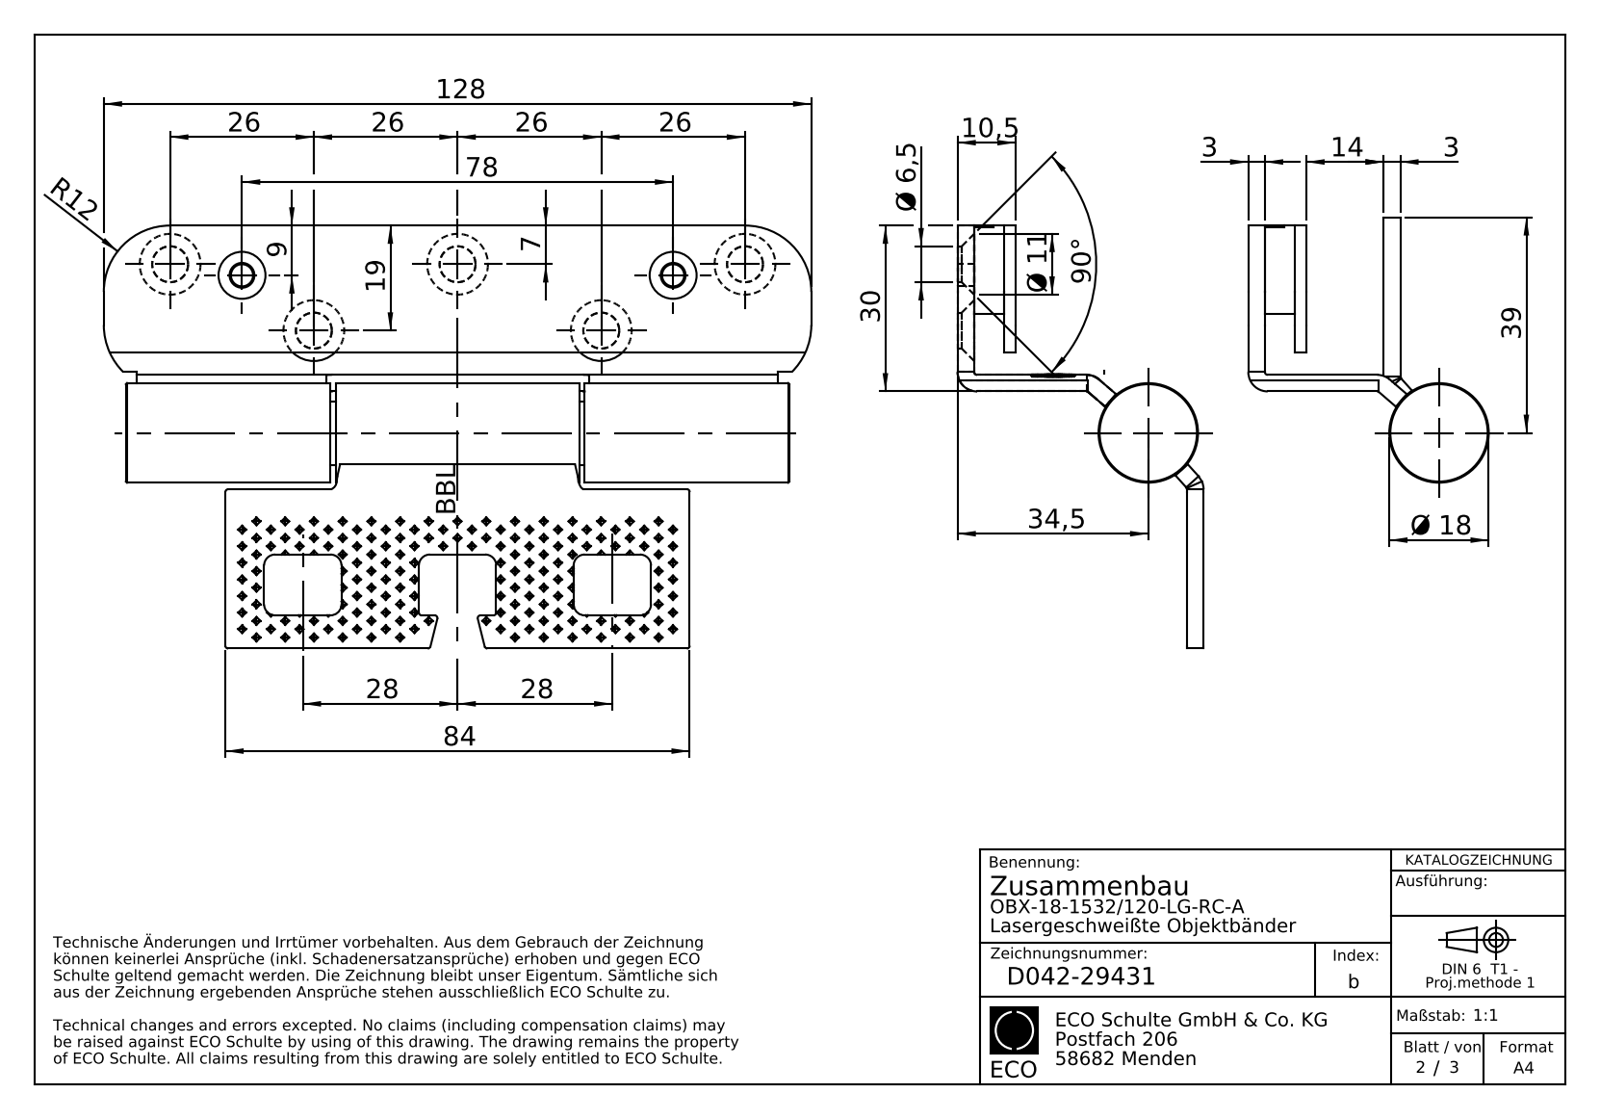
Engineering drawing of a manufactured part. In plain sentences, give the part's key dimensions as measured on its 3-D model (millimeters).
The part is named "B01572; D043-24287; D044-14308; D043-25258 (+6 more)". Its 3-D file was written by "SolidWorks 2020 (CONFIG_CONTROL_DESIGN)". It is 13 solids with 1925 faces: 1666 planar, 154 cylindrical and 105 other. Overall it measures 128 by 48 by 43.5 millimeters. Its volume is 65 338 cubic millimeters and its surface area 46 317 square millimeters. Round holes: 5 of diameter 6.5, 2 of diameter 2, 2 of diameter 4, 2 of diameter 5, 1 of diameter 0.5, 1 of diameter 4.5, 1 of diameter 7.9. Round bosses or shafts: 1 of diameter 18, 1 of diameter 12, 1 of diameter 11.8, 1 of diameter 11.5, 1 of diameter 7.7, 1 of diameter 4, 1 of diameter 1.65. Partial cylindrical surfaces (rounded edges, fillets, slot ends): 13 of radius 0.5, 10 of radius 2, 6 of radius 0.25, 4 of radius 12, 3 of radius 3.5, 2 of radius 0.68, 2 of radius 1, 2 of radius 2.1. The main face-to-face distances are 3, 2, 24.5, 5.5, 8.5, 14, 16, 7.5, 10.5, 4. The hole center spacings are 28.64, 52, 13.15, 16.4, 39.05, 65.76, 78.92, 91.02.
